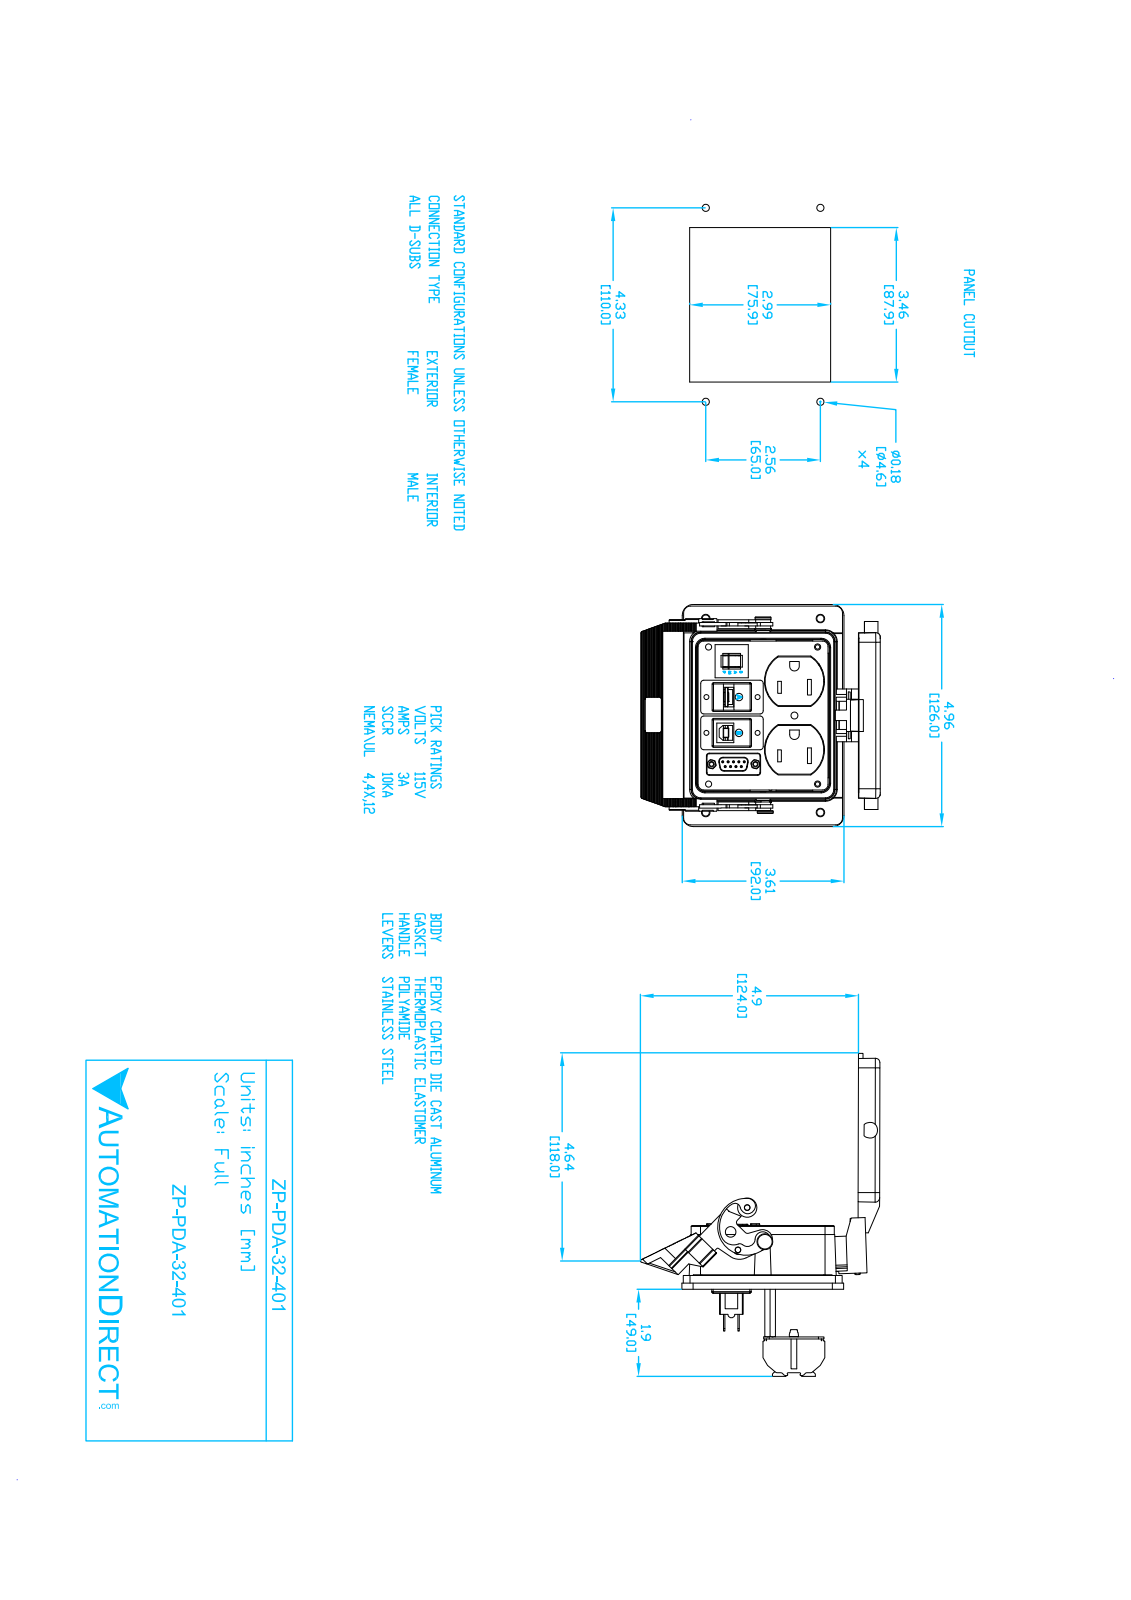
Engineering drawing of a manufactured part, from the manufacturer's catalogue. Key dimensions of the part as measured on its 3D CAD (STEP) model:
Part name (STEP PRODUCT): ZP-PDA-32-401
STEP written by: SolidWorks 2017 (AUTOMOTIVE_DESIGN)
Units: inches
Bodies: 1 solid, 4562 faces (2895 planar, 893 cylindrical, 774 other)
Overall size (bounding box): 6.857 × 5.313 × 4.96
Volume: 14 in³ · Surface area: 193.9 in²
Round holes (diameter × count): ⌀0.045 ×9, ⌀0.098 ×8, ⌀0.144 ×8, ⌀0.173 ×6, ⌀0.16 ×4, ⌀0.19 ×4, ⌀0.091 ×3, ⌀0.09 ×2, ⌀0.12 ×2, ⌀0.122 ×2, ⌀0.126 ×2, ⌀0.134 ×2
Round bosses / shafts (diameter × count): ⌀0.038 ×9, ⌀0.22 ×6, ⌀0.118 ×6, ⌀0.226 ×4, ⌀0.205 ×3, ⌀0.354 ×2, ⌀0.344 ×2, ⌀0.109 ×2
Partial cylindrical surfaces — rounded edges, fillets, slot ends (radius × count): R0.012 ×48, R0.02 ×30, R0.02 ×22, R0.008 ×20, R0.1 ×18, R0.006 ×16, R0.025 ×12, R0.25 ×12
Main face-to-face distances: 0.135, 0.907, 0.847, 0.06, 0.73, 1.577, 1.637, 0.977, 0.247, 0.6
Hole centre spacings: 0.12, 0.472, 3.071, 0.236, 0.633, 1.063, 1.287, 1.378
